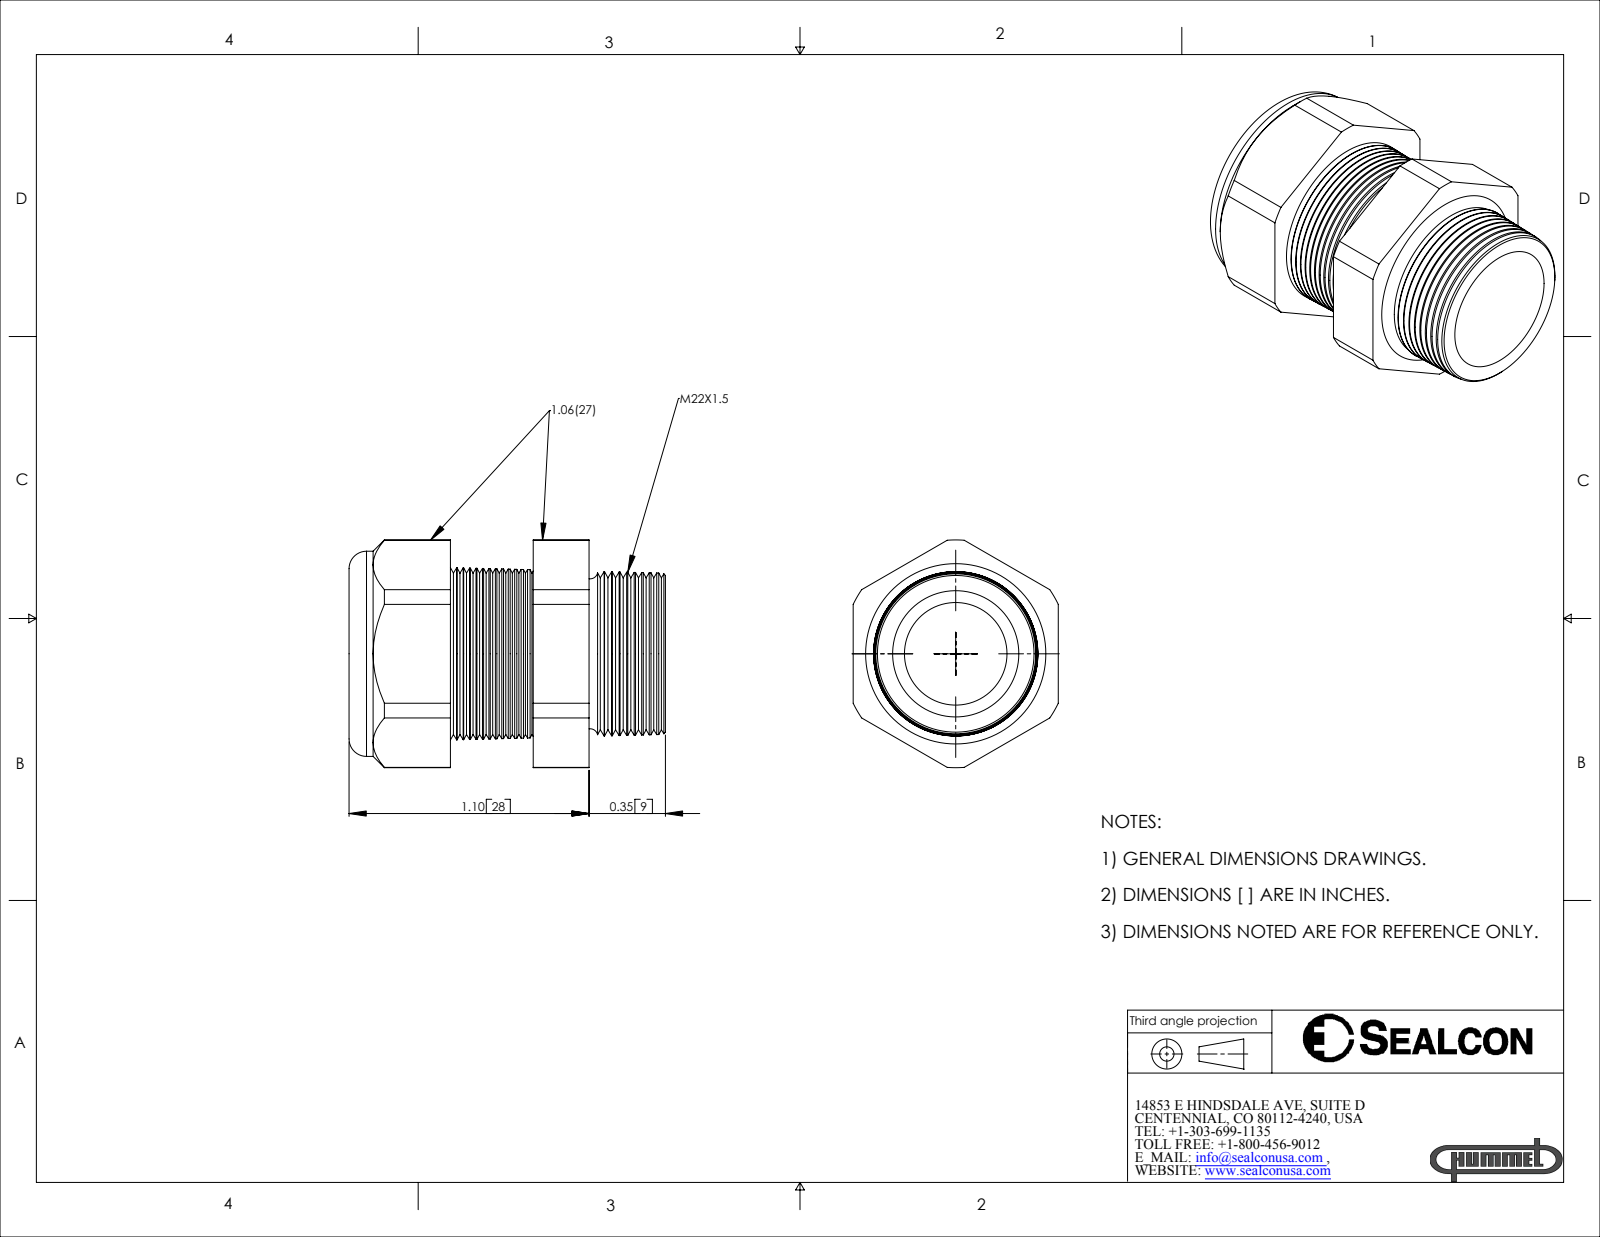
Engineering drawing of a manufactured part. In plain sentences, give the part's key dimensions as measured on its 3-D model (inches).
The part is named "CD22MP-BK". Its 3-D file was written by "SolidWorks 2007 (CONFIG_CONTROL_DESIGN)". It is 2 solids with 186 faces: 20 planar, 20 cylindrical and 146 other. Overall it measures 1.45 by 1.043 by 0.94 inches. Its volume is 0.595 cubic inches and its surface area 10.02 square inches. Round holes: 1 of diameter 0.45, 1 of diameter 0.47. Round bosses or shafts: 1 of diameter 0.94. Partial cylindrical surfaces (rounded edges, fillets, slot ends): 1 of radius 0.522. The main face-to-face distances are 0.94, 0.844, 0.465, 0.38, 1.1, 0.635, 0.256, 0.25, 0.215, 0.594.
